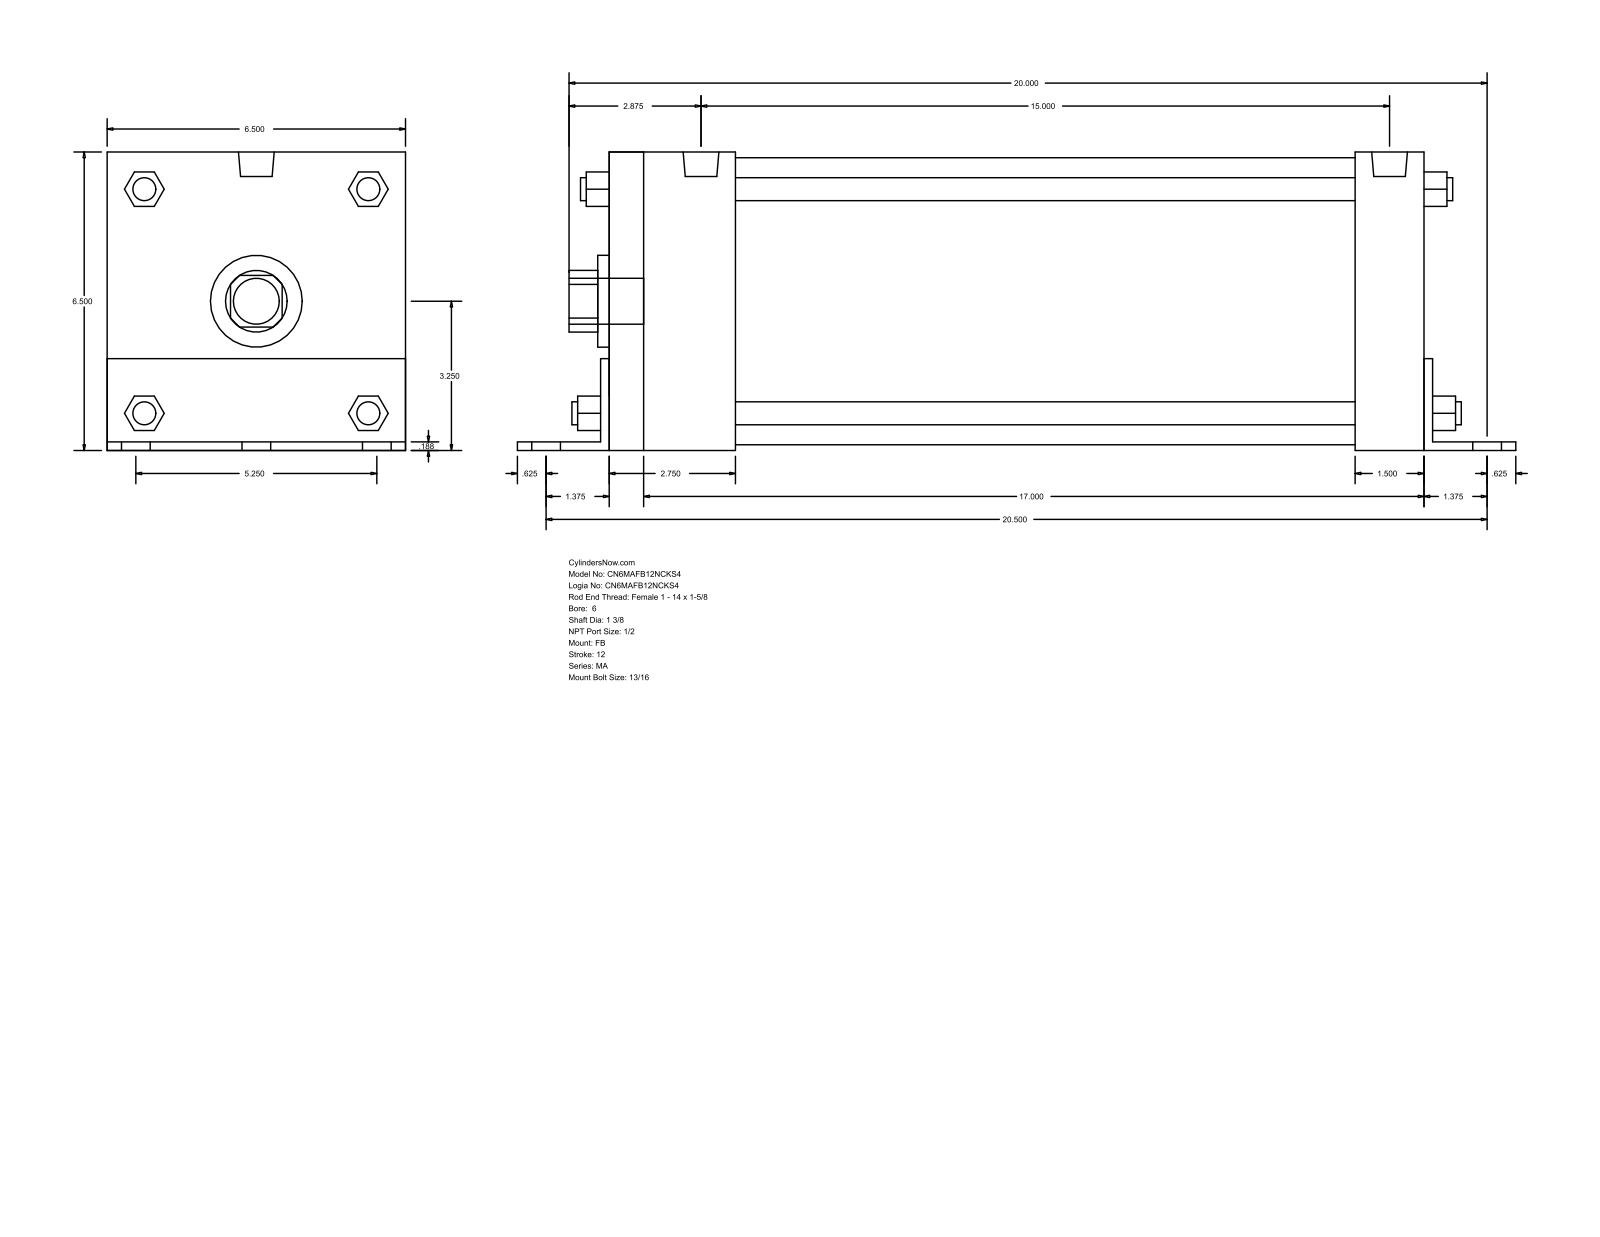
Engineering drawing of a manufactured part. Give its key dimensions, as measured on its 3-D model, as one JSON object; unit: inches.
{"part_name": "MA_FB__0600_1.375", "step_written_by": "GSSL Pune (CONFIG_CONTROL_DESIGN)", "units": "inches", "bodies": {"solids": 0, "faces": 140, "planar": 105, "cylindrical": 35, "other": 0}, "overall_size": [21.625, 6.502, 6.5], "round_holes": [[1.375, 1], [2, 1], [6.25, 1]], "round_bosses_or_shafts": [[0.813, 6], [0.687, 4], [0.5, 4], [0.778, 2], [1, 1]], "partial_cylinders_radius": [[0.672, 1], [1.262, 1]], "face_to_face_distances": [6.5, 0.187, 17.625, 6.502, 0.185, 6.315, 0.188, 1.5, 17.813, 18]}
